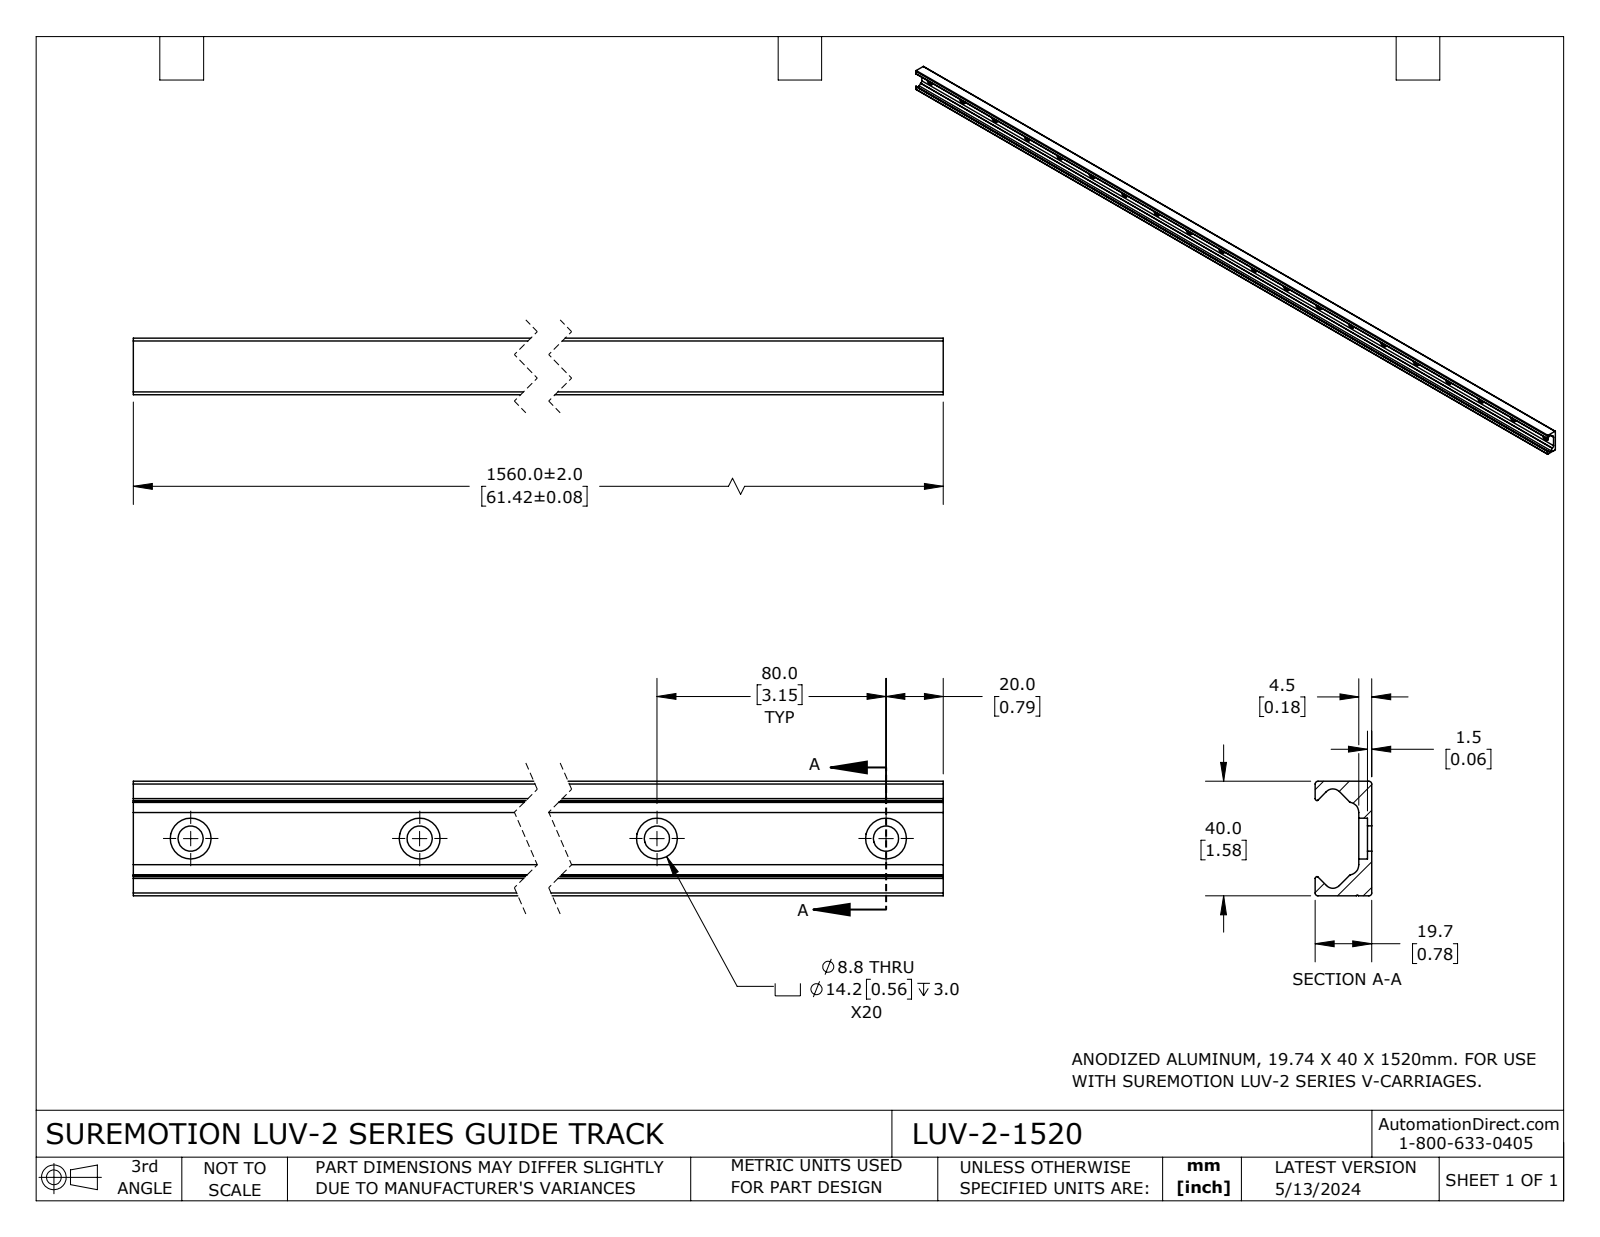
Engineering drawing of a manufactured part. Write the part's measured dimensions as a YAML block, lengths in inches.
part_name: "LUV-2-1520"
step_written_by: "SolidWorks 2023 (CONFIG_CONTROL_DESIGN)"
units: inches
bodies: {solids: 1, faces: 128, planar: 33, cylindrical: 95, other: 0}
overall_size: [61.417, 1.575, 0.777]
volume: 31.66
surface_area: 366.6
round_holes:
  - {diameter: 0.347, count: 20}
  - {diameter: 0.561, count: 20}
partial_cylinders:
  - {radius: 0.039, count: 4}
  - {radius: 0.017, count: 2}
  - {radius: 0.025, count: 2}
  - {radius: 0.025, count: 2}
  - {radius: 0.125, count: 2}
  - {radius: 0.142, count: 2}
  - {radius: 0.013, count: 1}
face_to_face_distances: [1.576, 0.177, 0.777, 0.6, 1.038, 0.059, 0.118, 0.718, 61.417]
hole_center_spacings: [3.15, 6.299, 9.449, 12.598, 15.748, 18.898, 22.047, 25.197]
